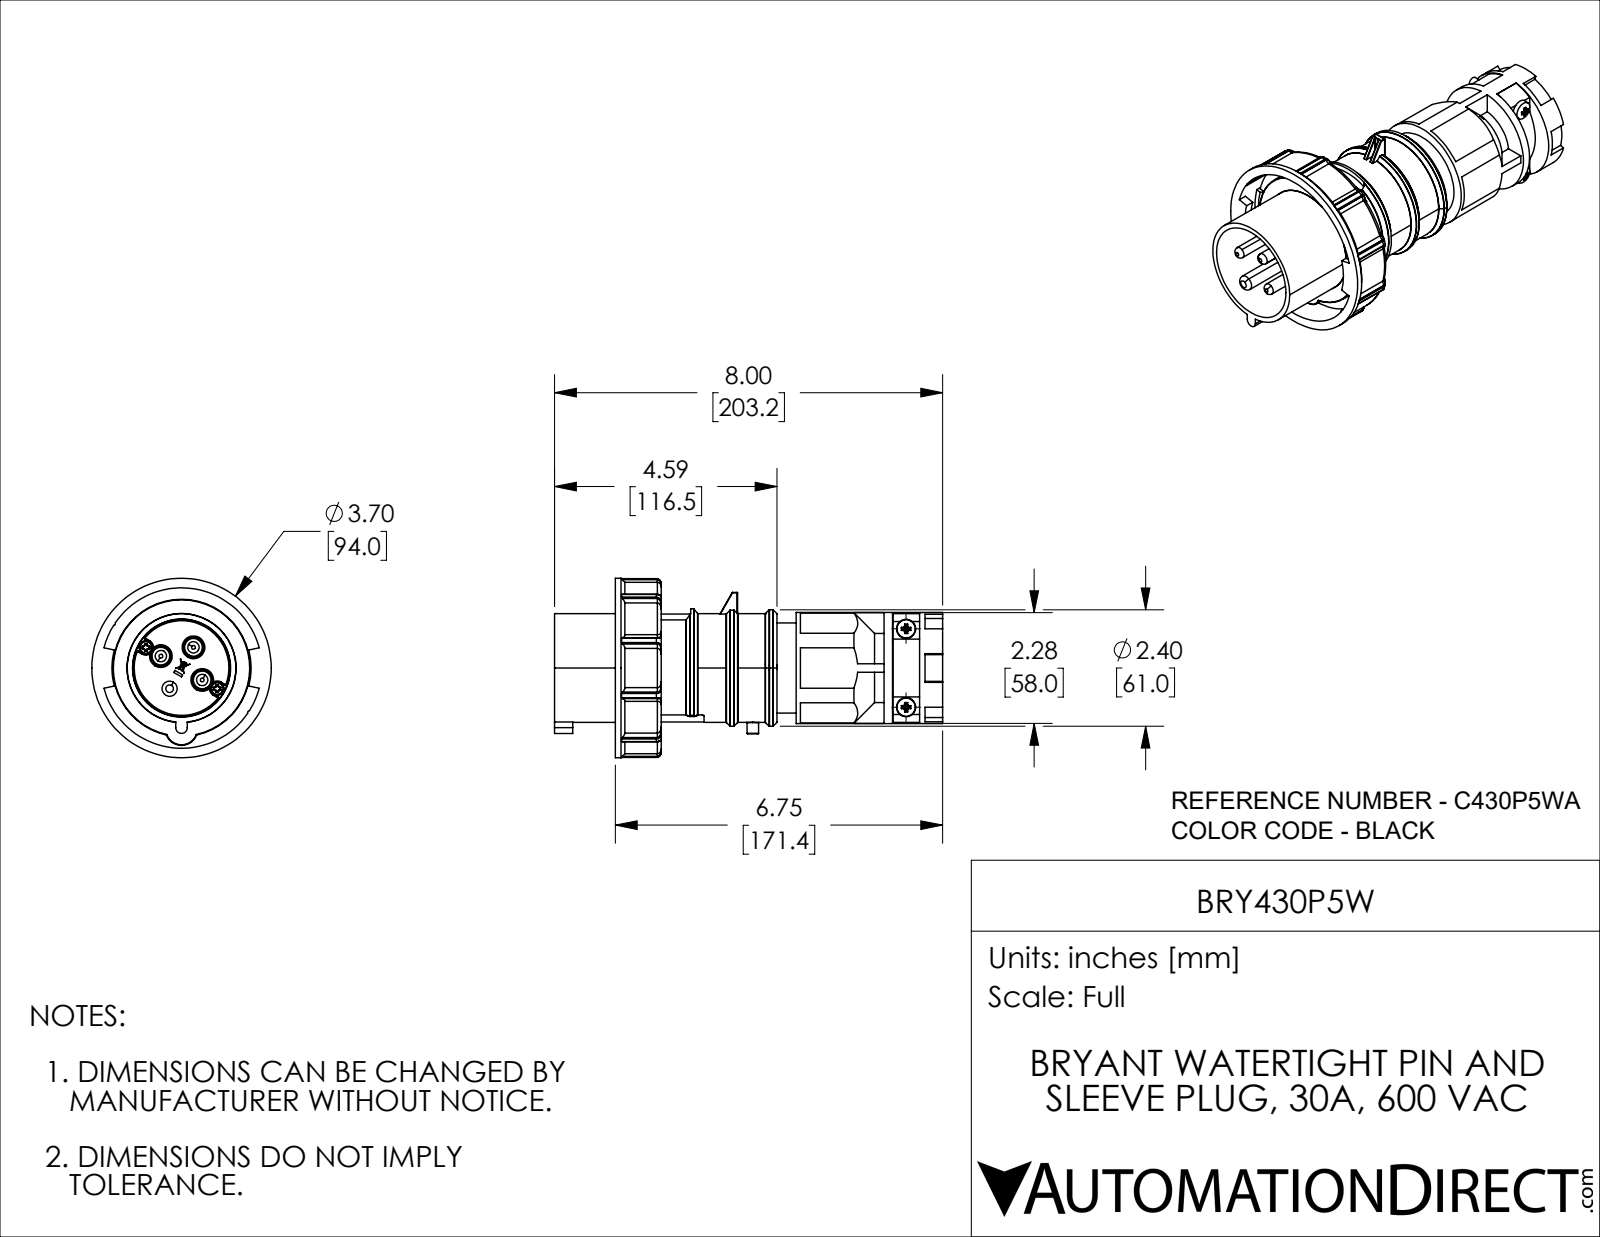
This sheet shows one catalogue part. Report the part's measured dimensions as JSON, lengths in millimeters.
{"part_name": "BRY430P5W", "step_written_by": "SolidWorks 2021 (CONFIG_CONTROL_DESIGN)", "units": "millimeters", "bodies": {"solids": 10, "faces": 920, "planar": 332, "cylindrical": 281, "other": 307}, "overall_size": [203.23, 94, 94], "volume_mm3": 404841, "surface_area_mm2": 98258, "round_holes": [[5, 2], [0.51, 1], [3.1, 1], [29.5, 1], [36.5, 1], [49.04, 1], [51.1, 1], [84, 1]], "round_bosses_or_shafts": [[6, 4], [94, 1], [72, 1], [62, 1], [61, 1], [58.2, 1], [57, 1], [56.9, 1]], "partial_cylinders_radius": [[0.5, 28], [2.5, 20], [0.25, 13], [1, 6], [3, 3], [0.3, 2], [1.75, 2], [3.55, 2]], "face_to_face_distances": [70.73, 4.5, 64.7, 135.43, 18.7, 10, 143.73, 79.03, 8.3, 54.2], "hole_center_spacings": [1.18, 41]}
